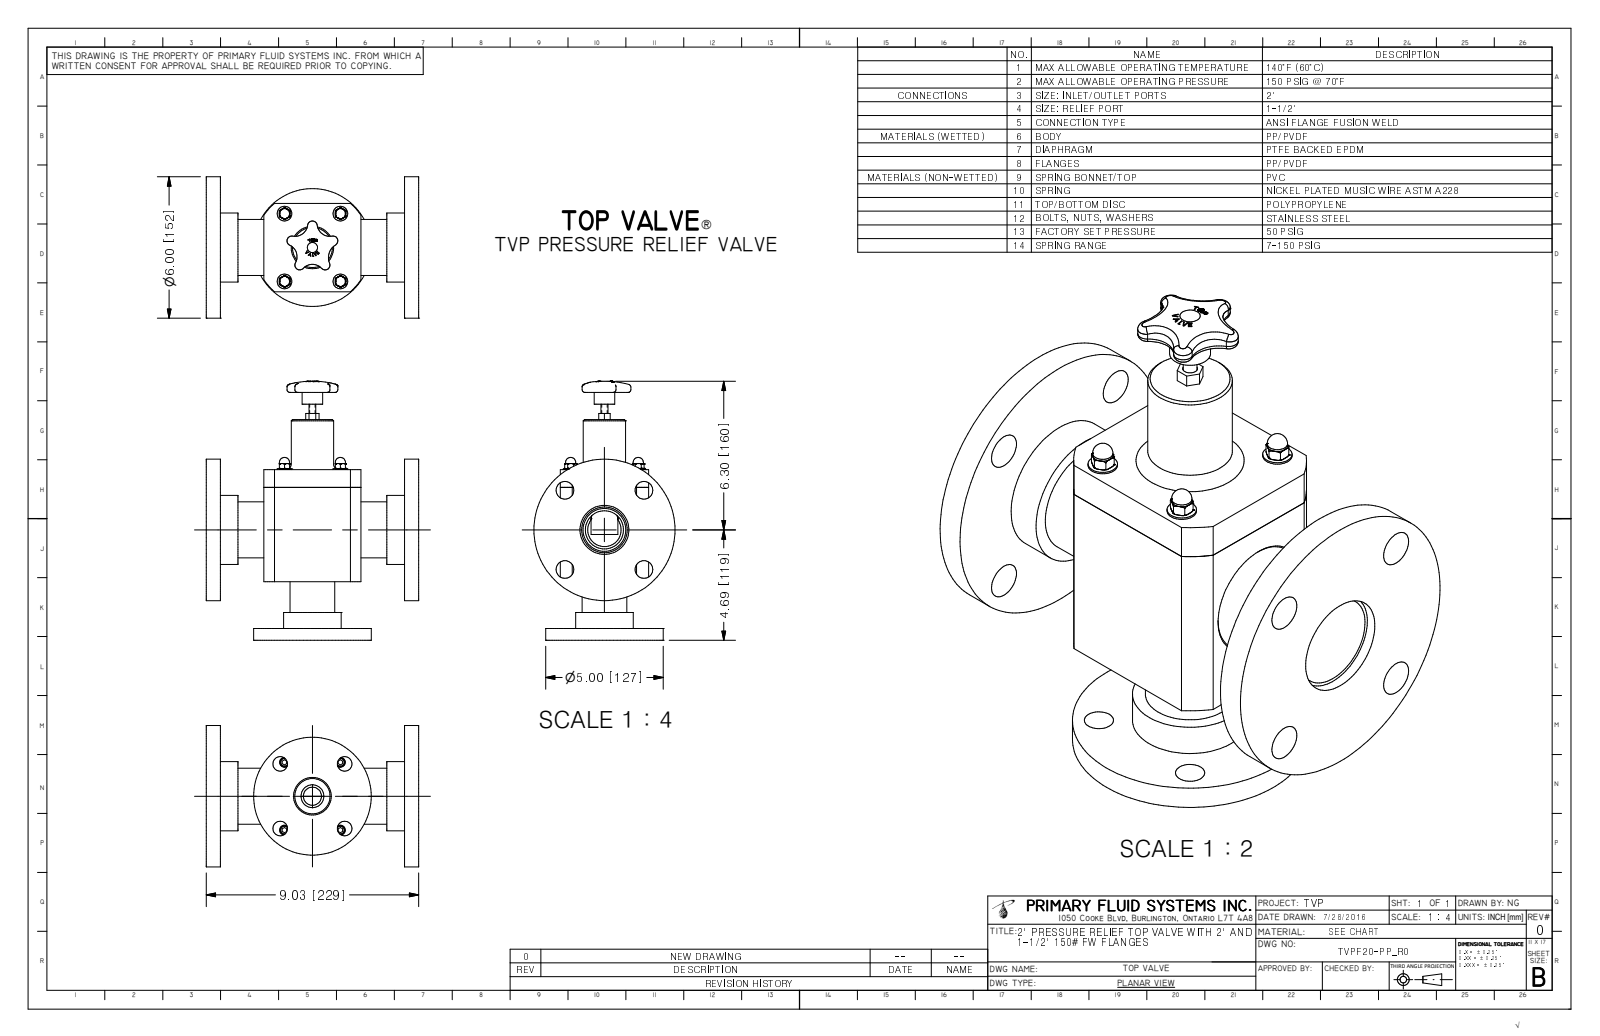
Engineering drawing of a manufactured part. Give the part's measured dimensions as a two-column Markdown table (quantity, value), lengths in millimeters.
| quantity | value |
| --- | --- |
| part name | TVPF20-PP_R0 |
| STEP written by | Autodesk Inventor 2009 (AUTOMOTIVE_DESIGN) |
| units | millimeters |
| bodies | 1 solid, 376 faces (157 planar, 70 cylindrical, 149 other) |
| overall size | 279.1 × 229.4 × 152.4 |
| volume | 1 989 000 mm³ |
| surface area | 252 800 mm² |
| round holes (diameter × count) | 4.4 × 4, 15.7 × 4, 19.1 × 4, 38.1 × 1, 40.6 × 1, 49.3 × 1, 52.8 × 1 |
| round bosses / shafts (diameter × count) | 15.9 × 4, 11 × 4, 9.5 × 4, 152.4 × 1, 127 × 1, 74.4 × 1, 62.2 × 1, 60.3 × 1 |
| partial cylindrical surfaces (radius × count) | 2.2 × 5, 5.2 × 5, 13.6 × 4, 16.7 × 4, 15.9 × 1, 18.9 × 1, 62.9 × 1 |
| main face-to-face distances | 15.2, 214.1, 229.4, 198.9, 62.3, 167.1, 47, 151.8, 95.3, 12.7 |
| hole center spacings | 49.2, 60.3, 65, 69.6, 85.3, 4.9, 5, 47.3 |
